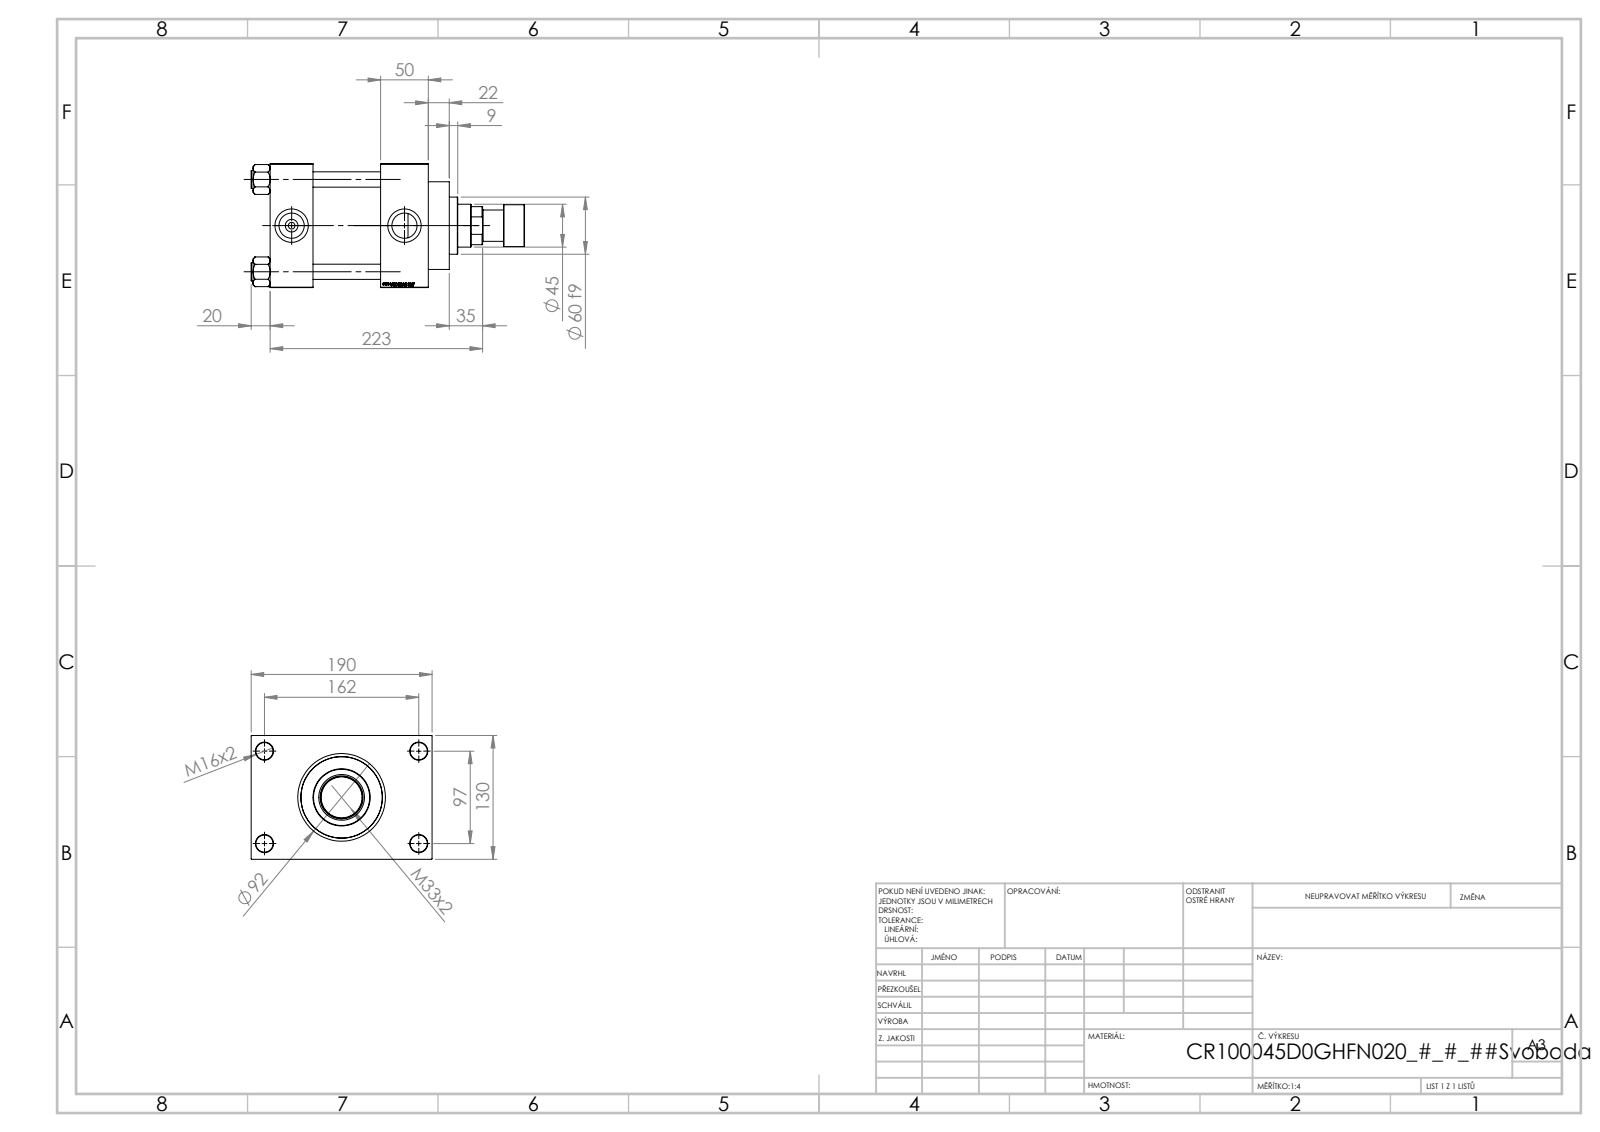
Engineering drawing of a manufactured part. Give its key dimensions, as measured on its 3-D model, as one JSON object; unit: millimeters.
{"part_name": "V215CR_D_TYCINKA; NUT_M5_D; V215CR_ROD_END_F; V215CR_VCP_D (+2 more)", "step_written_by": "SolidWorks 2019 (CONFIG_CONTROL_DESIGN)", "units": "millimeters", "bodies": {"solids": 12, "faces": 1164, "planar": 548, "cylindrical": 92, "other": 524}, "overall_size": [287, 190, 130], "volume_mm3": 2643000, "surface_area_mm2": 363256, "round_holes": [[16, 4], [18, 4], [7, 2], [26.44, 2], [35, 2], [31.5, 1], [45, 1], [48, 1], [76, 1], [85.5, 1], [100, 1]], "round_bosses_or_shafts": [[19, 4], [106, 1], [92, 1], [60, 1], [44, 1], [33, 1]], "face_to_face_distances": [130, 116, 45, 71, 166, 121, 50, 30, 160, 70], "hole_center_spacings": [32.55, 68.52, 94.41, 96.9, 102.27, 129.45, 161.73, 97]}
